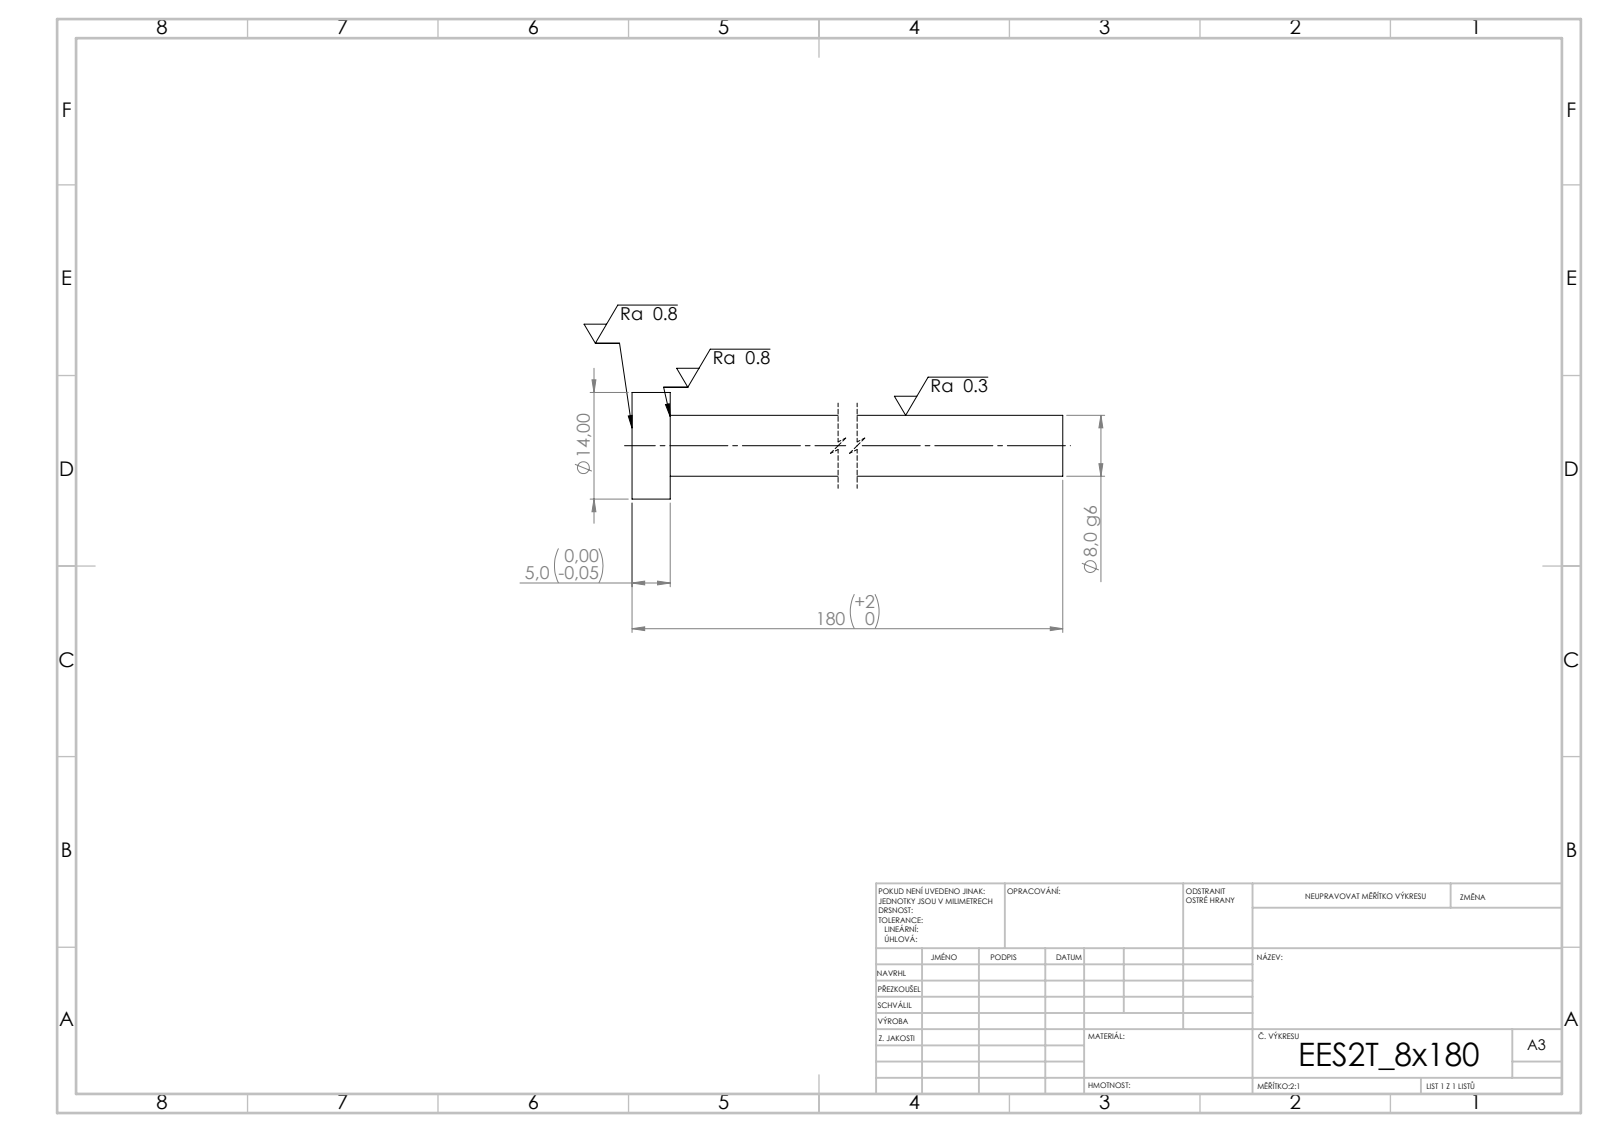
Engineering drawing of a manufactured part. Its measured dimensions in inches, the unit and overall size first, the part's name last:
Units: inches
Overall size (bounding box): 7.087 × 0.551 × 0.551
Round bosses / shafts (diameter × count): ⌀0.551 ×1, ⌀0.315 ×1
Main face-to-face distances: 0.197, 7.087, 6.89
Volume: 0.584 in³ · Surface area: 7.635 in²
Bodies: 1 solid, 7 faces (3 planar, 4 cylindrical, 0 other)
STEP written by: SolidWorks 2019 (CONFIG_CONTROL_DESIGN)
